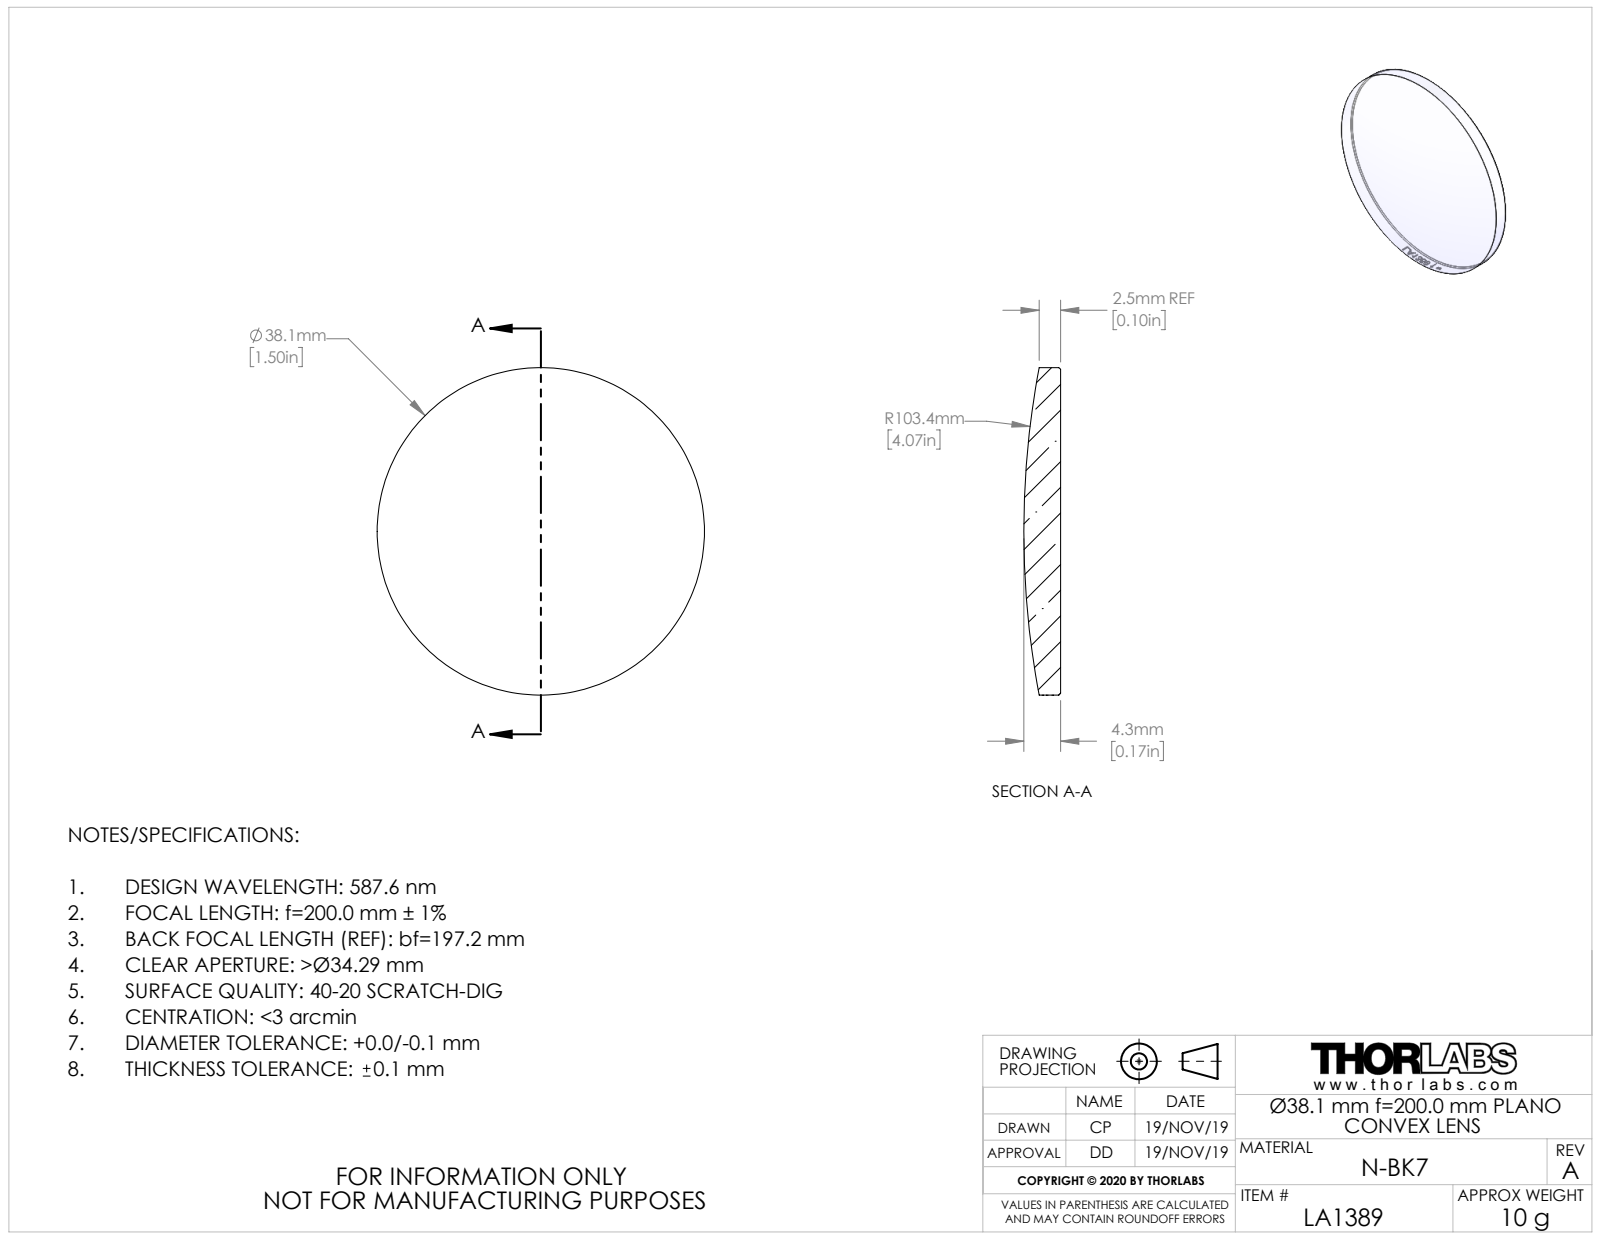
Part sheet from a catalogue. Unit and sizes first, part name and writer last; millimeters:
Units: millimetres
Overall size (bounding box): 38.1 × 38.1 × 4.27
Round bosses / shafts (diameter × count): ⌀38.1 ×1
Volume: 3 859 mm³ · Surface area: 2 575 mm²
Bodies: 1 solid, 21 faces (1 planar, 16 cylindrical, 4 other)
Part name (STEP PRODUCT): TTN200660-E0W
STEP written by: SolidWorks 2018 (CONFIG_CONTROL_DESIGN)
